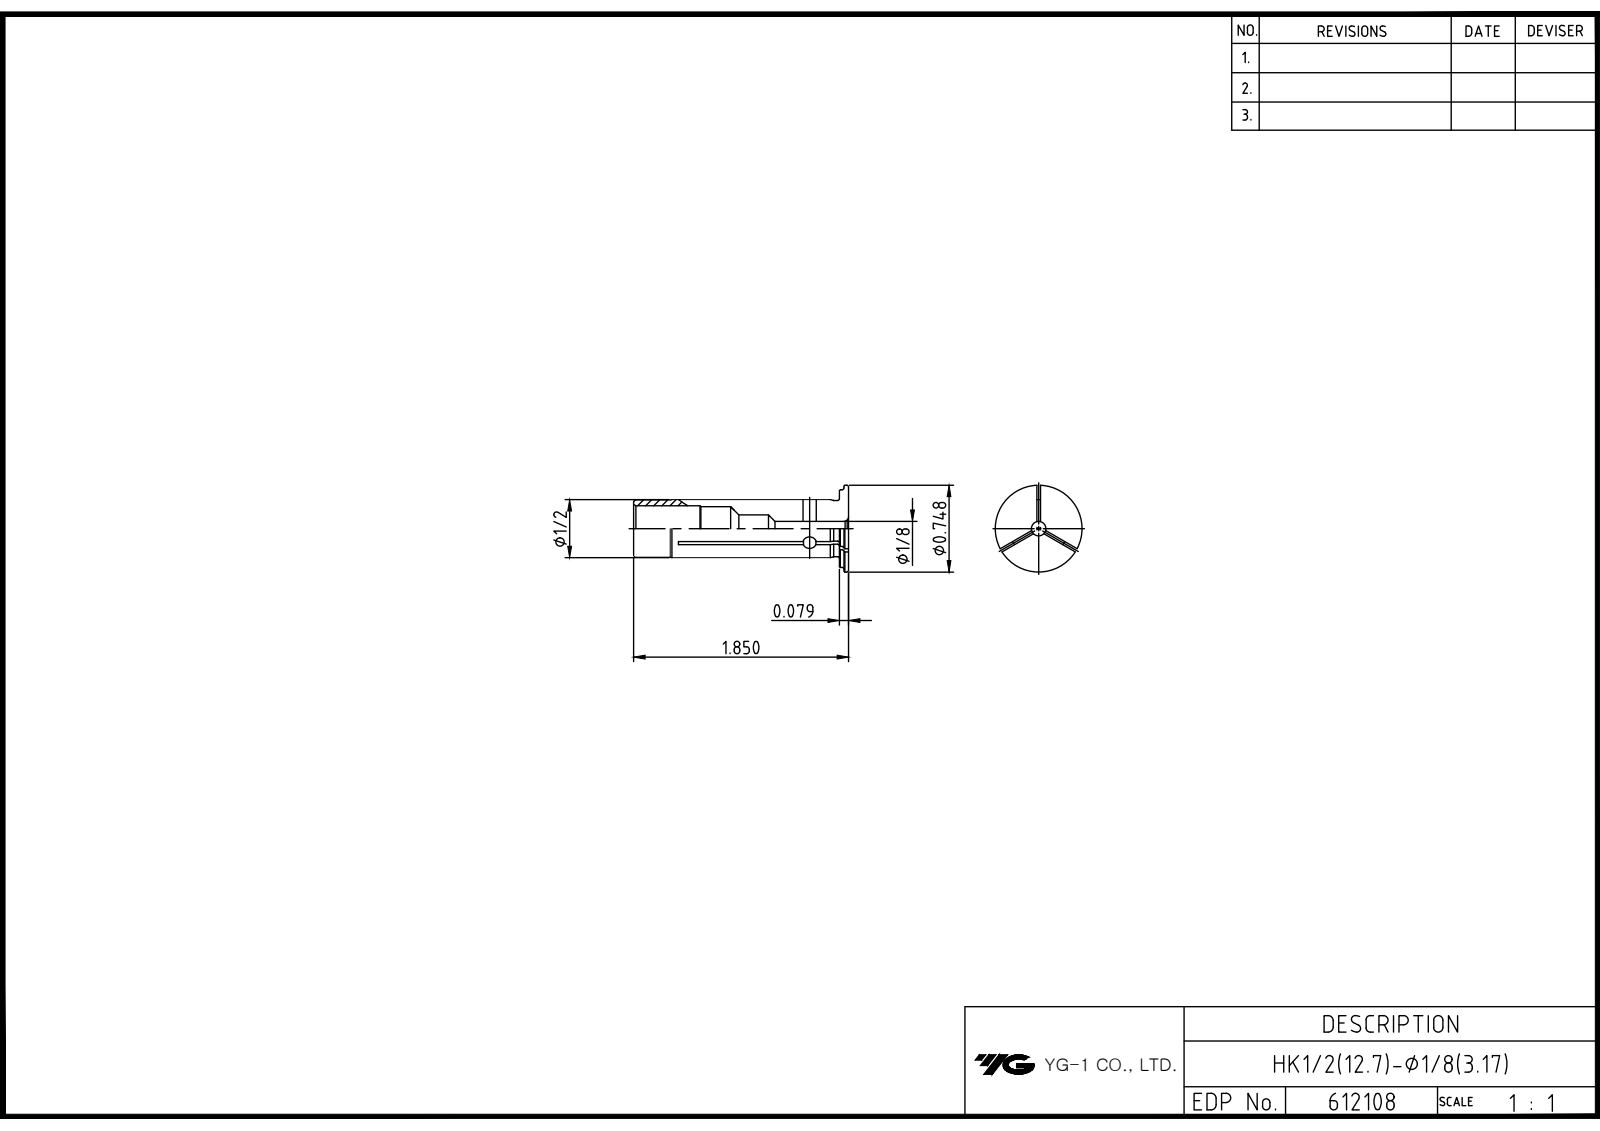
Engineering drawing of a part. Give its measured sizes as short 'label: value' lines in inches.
name: LO-HK12.7-3.175
written by: Autodesk Inventor 2022 (AUTOMOTIVE_DESIGN)
unit: in
bodies: 1 solid, 14 faces (4 planar, 7 cylindrical, 3 other)
size: 1.85 × 0.748 × 0.748
volume: 0.254 in³; area: 5.307 in²
holes: 1× ⌀0.125, 1× ⌀0.236, 1× ⌀0.378, 1× ⌀0.394
bosses: 1× ⌀0.748, 1× ⌀0.669, 1× ⌀0.5
face distances: 0.039, 0.079, 1.772, 1.811, 1.85
